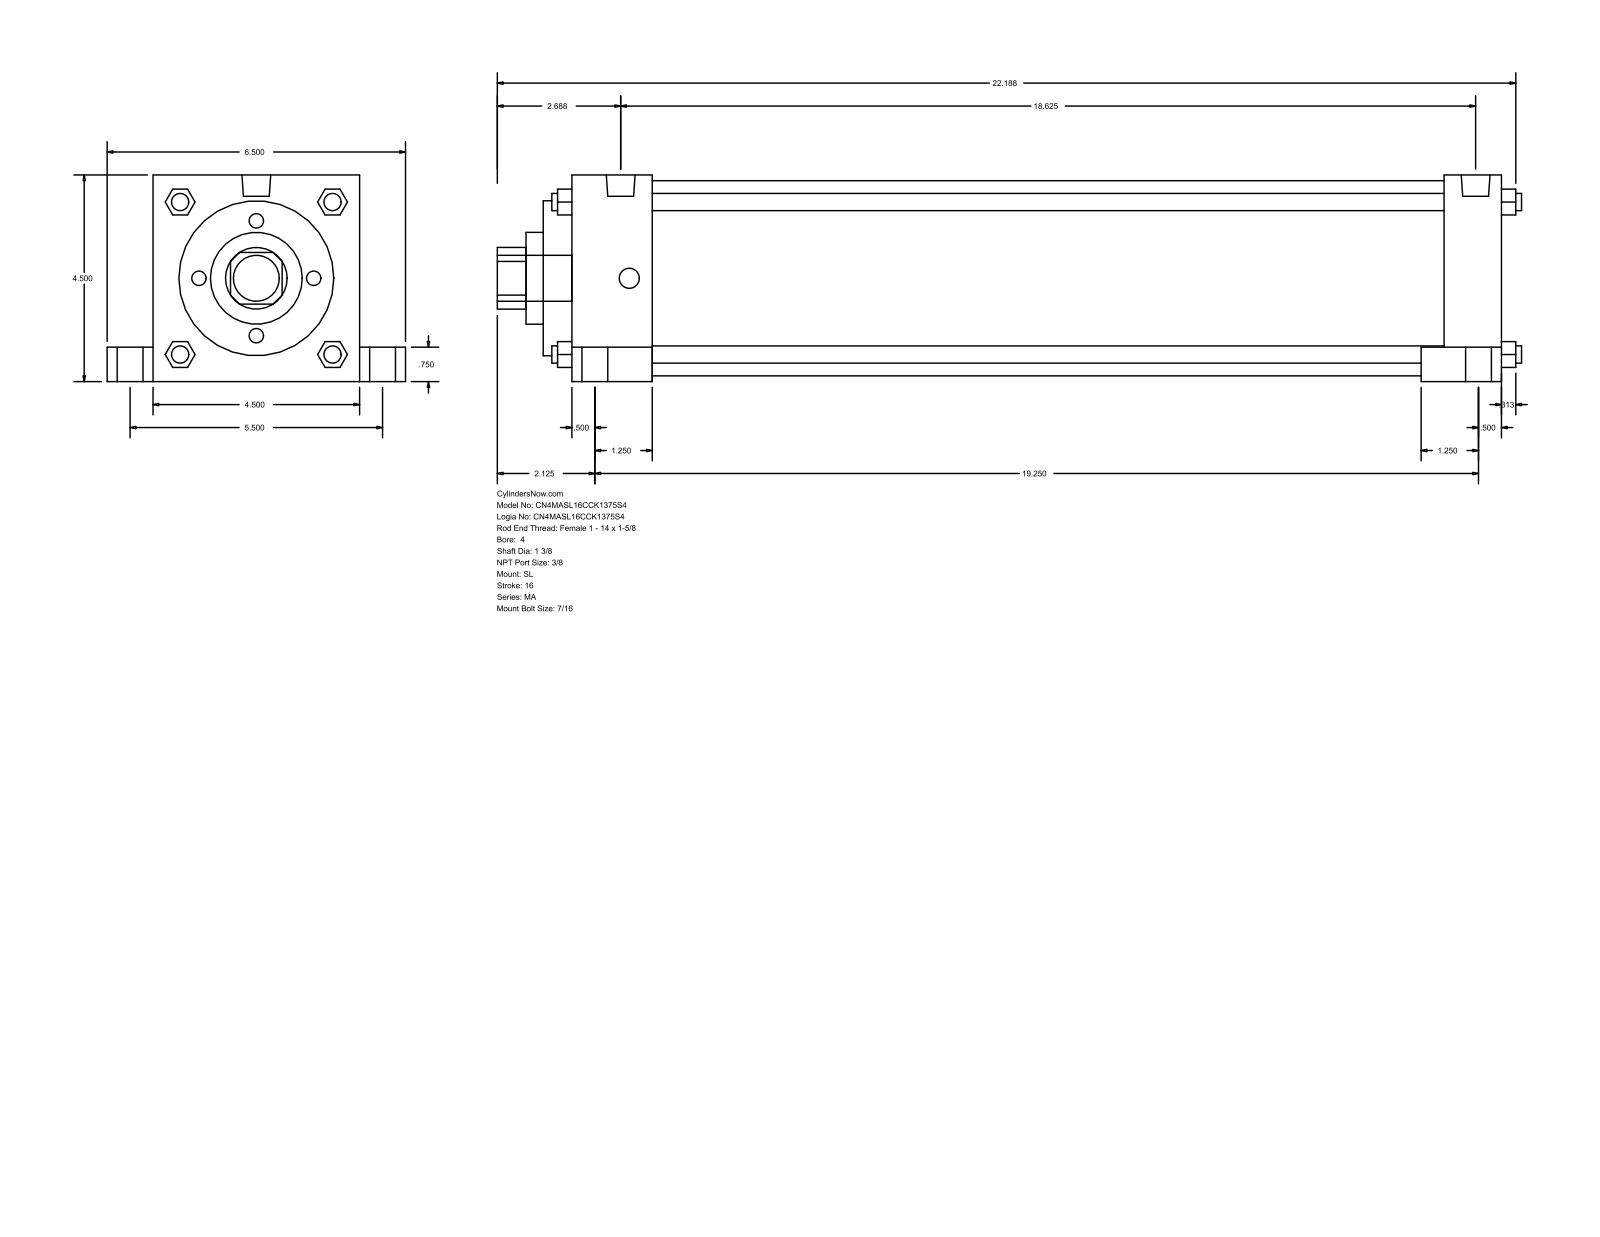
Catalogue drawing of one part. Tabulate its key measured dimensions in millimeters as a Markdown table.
| quantity | value |
| --- | --- |
| part name | MA_SL__0400_1.375 |
| STEP written by | GSSL Pune (CONFIG_CONTROL_DESIGN) |
| units | millimeters |
| bodies | 0 solids, 150 faces (113 planar, 37 cylindrical, 0 other) |
| overall size | 566.74 × 165.1 × 114.3 |
| round holes (diameter × count) | 34.92 × 1, 50.8 × 1, 85.72 × 1, 107.95 × 1 |
| round bosses / shafts (diameter × count) | 20.64 × 4, 14.29 × 4, 11.11 × 4, 9.53 × 4, 15.93 × 2, 25.4 × 1 |
| partial cylindrical surfaces (radius × count) | 17.06 × 1 |
| main face-to-face distances | 114.3, 514.35, 530.22, 15.87, 60.32, 44.45, 469.9, 498.48, 482.61, 438.16 |
